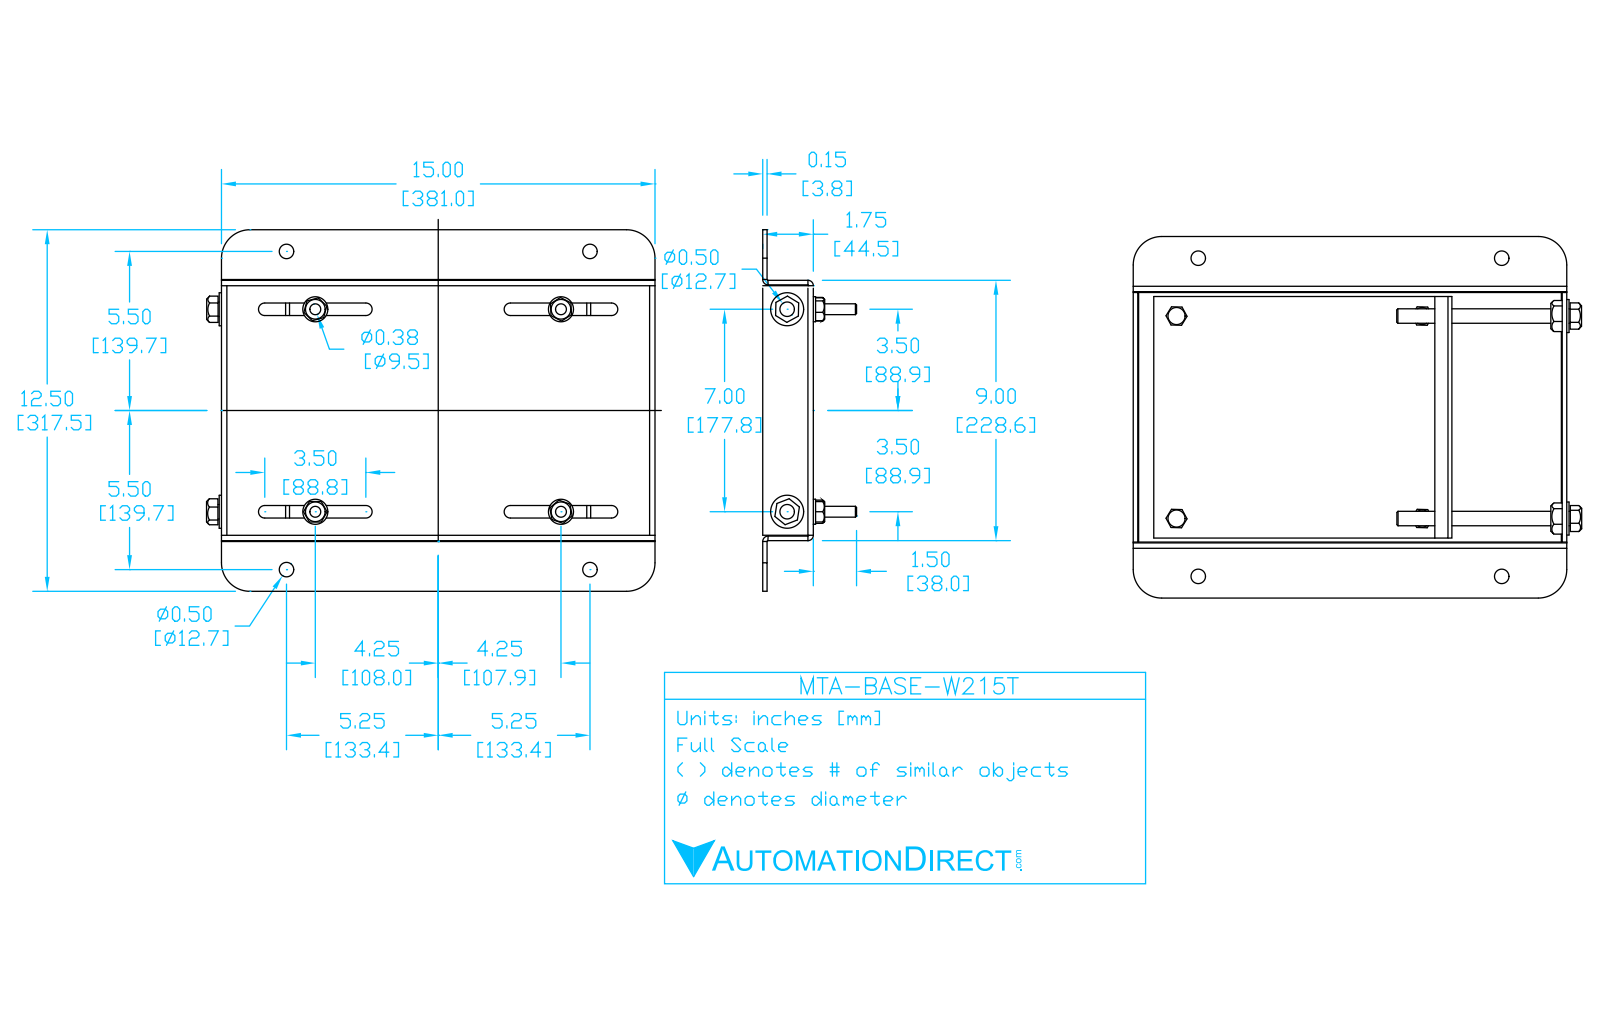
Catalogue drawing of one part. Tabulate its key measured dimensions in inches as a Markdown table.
| quantity | value |
| --- | --- |
| part name | W215T |
| STEP written by | SolidWorks 2017 (AUTOMOTIVE_DESIGN) |
| units | inches |
| bodies | 22 solids, 354 faces (178 planar, 104 cylindrical, 72 other) |
| overall size | 15.551 × 12.5 × 3.236 |
| volume | 55.52 in³ |
| surface area | 786 in² |
| round holes (diameter × count) | 0.5 × 6, 0.375 × 4, 0.378 × 4, 0.531 × 2, 0.551 × 2, 0.63 × 2 |
| round bosses / shafts (diameter × count) | 0.866 × 4, 1.142 × 2 |
| partial cylindrical surfaces (radius × count) | 0.029 × 8, 0.217 × 8, 0.186 × 6, 0.984 × 4, 0.135 × 2 |
| main face-to-face distances | 0.157, 1.593, 0.106, 0.264, 1.75, 1.486, 1.435, 1.329, 8.843, 14.843 |
| hole center spacings | 7, 2.137, 3.402, 8.002, 8.5, 9.031, 9.411, 10.5 |
